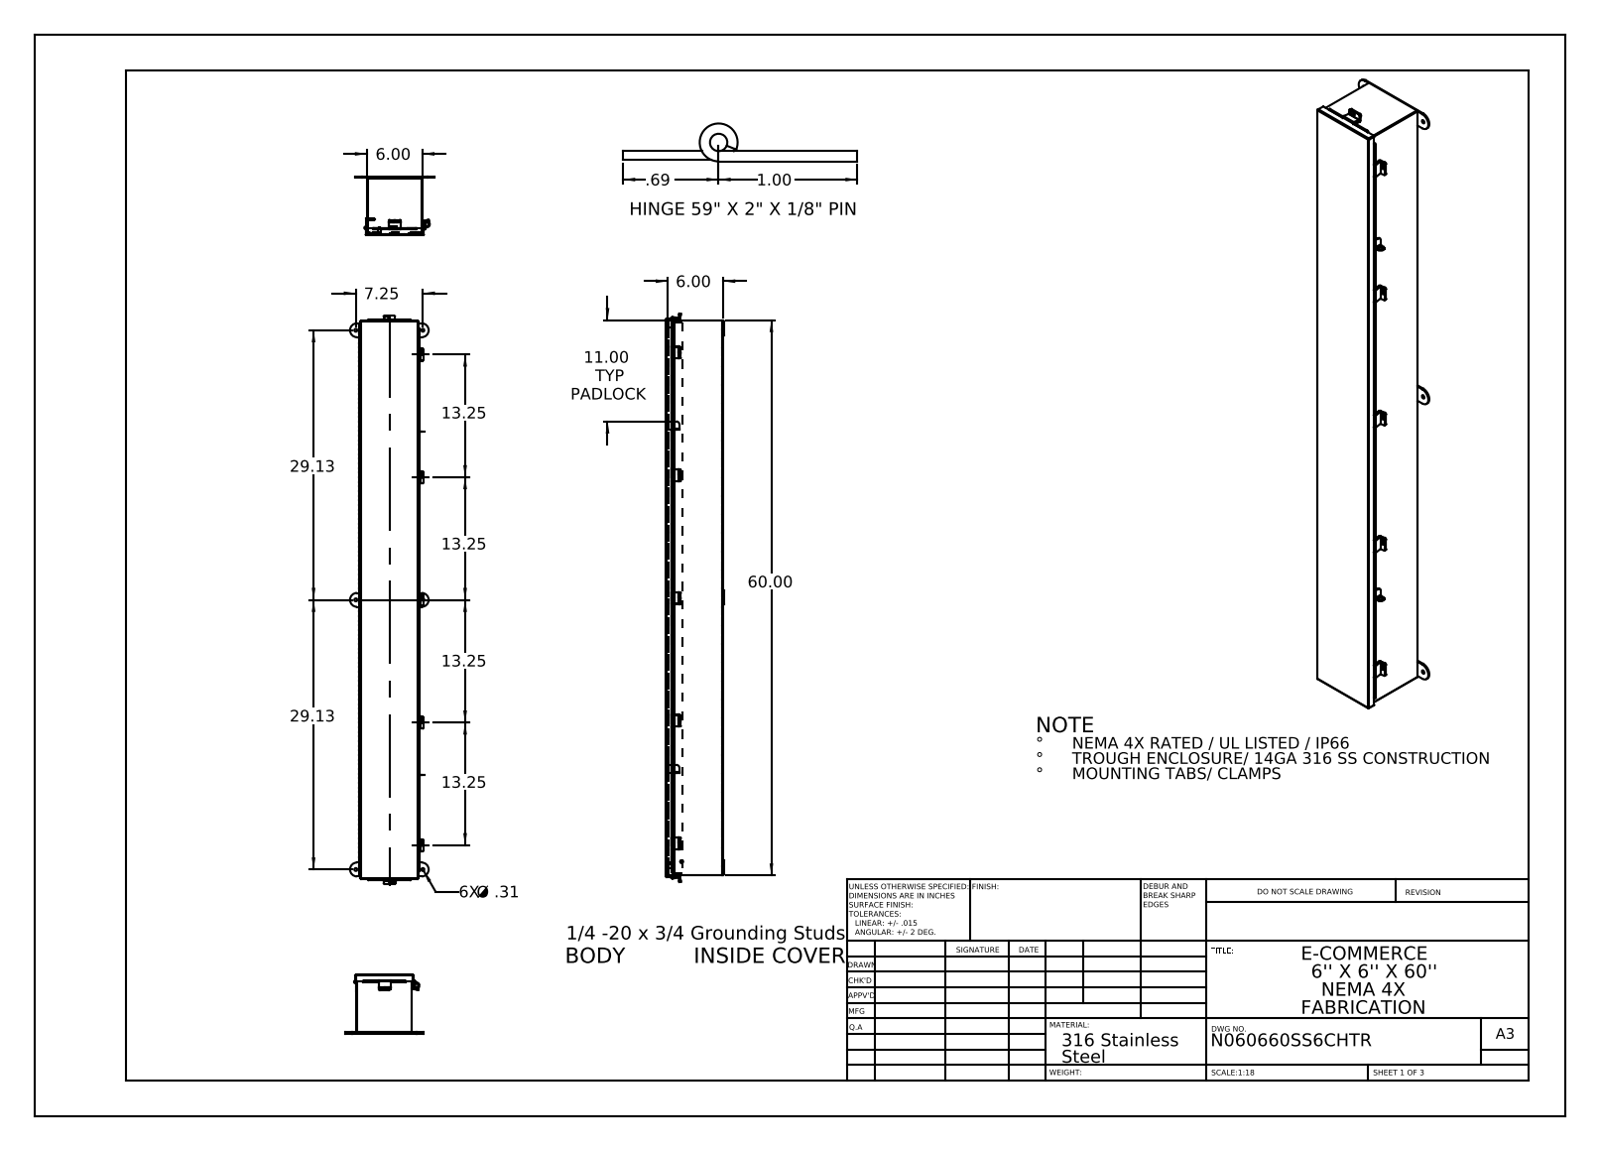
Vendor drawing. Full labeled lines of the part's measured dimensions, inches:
Part name (STEP PRODUCT): N060660SSCHTR JIC Mounting Bracket; N060660SSCHTR JIC Top; N060660SSCHTR JIC Bottom; N060660SSCHTR JIC Clamp Bracket (+8 more)
STEP written by: SolidWorks 2013 (CONFIG_CONTROL_DESIGN)
Units: inches
Bodies: 27 solids, 1681 faces (1002 planar, 659 cylindrical, 20 other)
Overall size (bounding box): 61.407 × 8.5 × 6.337
Volume: 137.8 in³ · Surface area: 3 713 in²
Round holes (diameter × count): ⌀0.25 ×7, ⌀0.313 ×6, ⌀0.125 ×1, ⌀0.125 ×1, ⌀0.375 ×1
Round bosses / shafts (diameter × count): ⌀0.315 ×2, ⌀0.236 ×2, ⌀0.273 ×1, ⌀0.25 ×1
Partial cylindrical surfaces — rounded edges, fillets, slot ends (radius × count): R0.125 ×27, R0.133 ×14, R0.009 ×12, R0.013 ×10, R0.088 ×10, R0.083 ×6, R0.1 ×6, R0.75 ×6
Main face-to-face distances: 0.075, 5.925, 6.128, 6, 5.85, 6.203, 6.053, 0.149, 6.074, 0.074
Hole centre spacings: 13.25, 29.125, 7.25, 26.5, 30.014, 30.014, 39.75, 58.25
